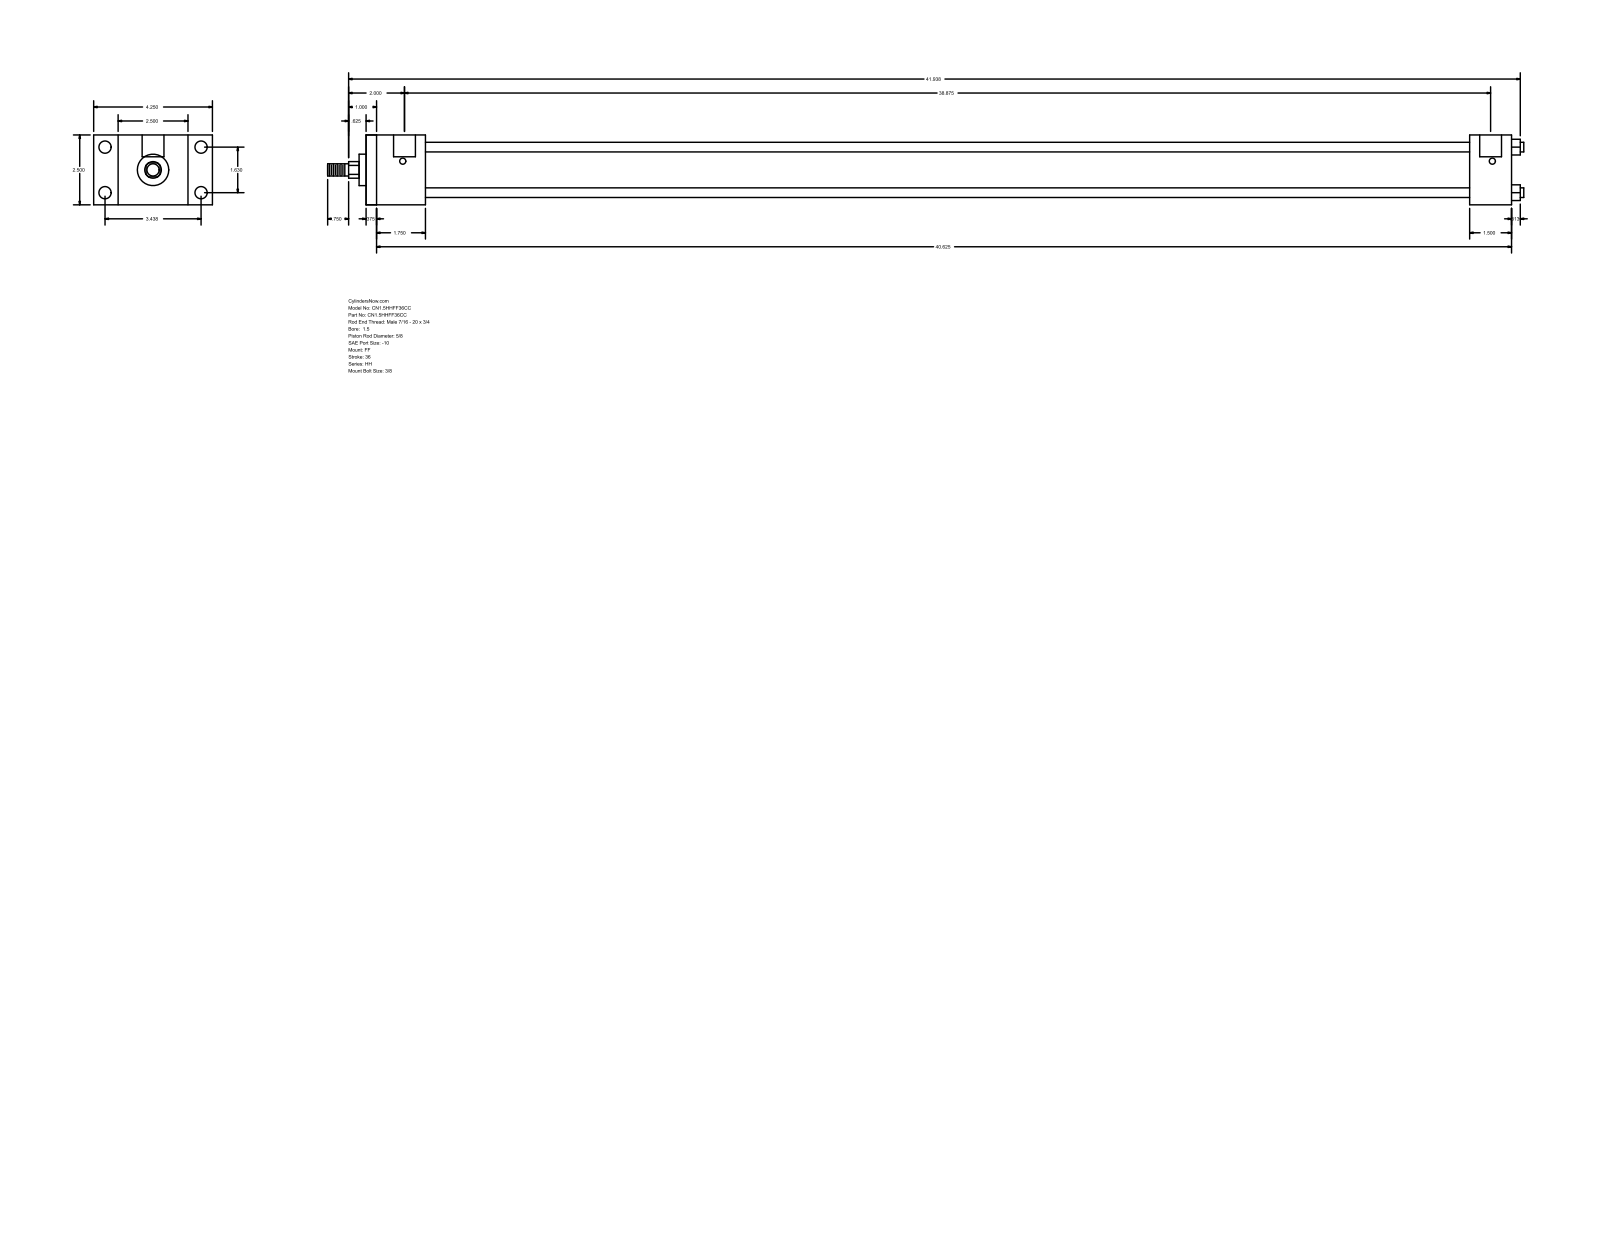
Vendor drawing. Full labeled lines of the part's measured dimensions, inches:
Part name (STEP PRODUCT): HH_FF__0150_0.625
STEP written by: GSSL Pune (CONFIG_CONTROL_DESIGN)
Units: inches
Bodies: 0 solids, 92 faces (64 planar, 28 cylindrical, 0 other)
Overall size (bounding box): 42.813 × 4.25 × 2.5
Round holes (diameter × count): ⌀0.219 ×4, ⌀0.438 ×4, ⌀0.781 ×2
Round bosses / shafts (diameter × count): ⌀0.345 ×4, ⌀1.75 ×1, ⌀1.125 ×1, ⌀0.625 ×1, ⌀0.437 ×1
Partial cylindrical surfaces — rounded edges, fillets, slot ends (radius × count): R0.297 ×1
Main face-to-face distances: 2.5, 41, 0.375, 40.625, 1.75, 2.125, 38.875, 39.5, 39.125, 37.375
Hole centre spacings: 0.063, 1.63, 3.438, 3.805, 38.937, 39, 38.875
